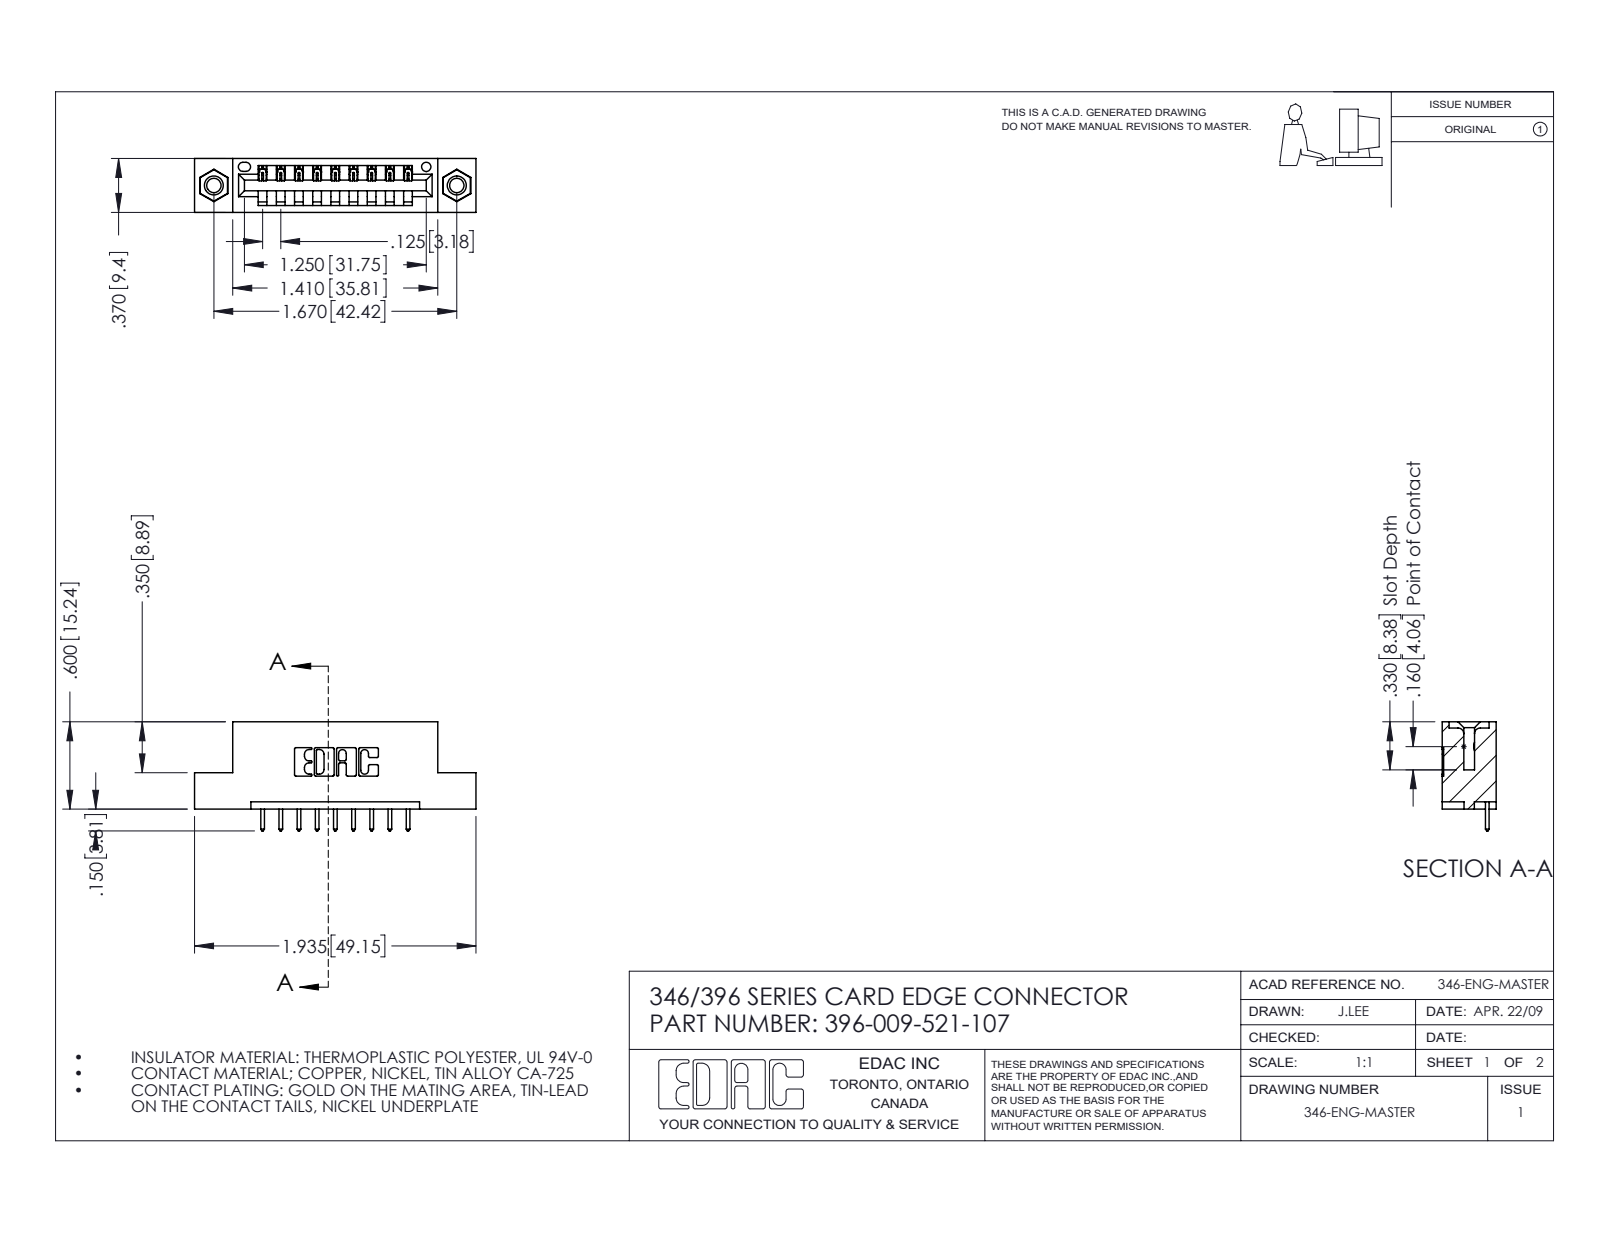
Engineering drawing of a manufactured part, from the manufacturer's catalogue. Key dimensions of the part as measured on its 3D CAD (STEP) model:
Part name (STEP PRODUCT): 345-292-001_345-293-121; 396-009-521-107; 346 Part_Flush Mounting Lugs - 0.156 Dia-TI; 345-250-001_345-250-005-103
STEP written by: SolidWorks 2016 (CONFIG_CONTROL_DESIGN)
Units: inches
Bodies: 12 solids, 704 faces (468 planar, 220 cylindrical, 16 other)
Overall size (bounding box): 1.935 × 0.75 × 0.37
Volume: 0.271 in³ · Surface area: 7.942 in²
Round holes (diameter × count): ⌀0.098 ×2, ⌀0.125 ×2, ⌀0.156 ×2, ⌀0.064 ×1
Round bosses / shafts (diameter × count): ⌀0.155 ×2
Partial cylindrical surfaces — rounded edges, fillets, slot ends (radius × count): R0.01 ×22, R0.006 ×18, R0.01 ×18, R0.007 ×6, R0.031 ×6, R0.026 ×3, R0.031 ×2, R0.04 ×2
Main face-to-face distances: 0.25, 0.37, 0.048, 0.322, 0.148, 0.222, 0.1, 0.174, 0.072, 0.298
Hole centre spacings: 0.246, 1.465, 1.67
